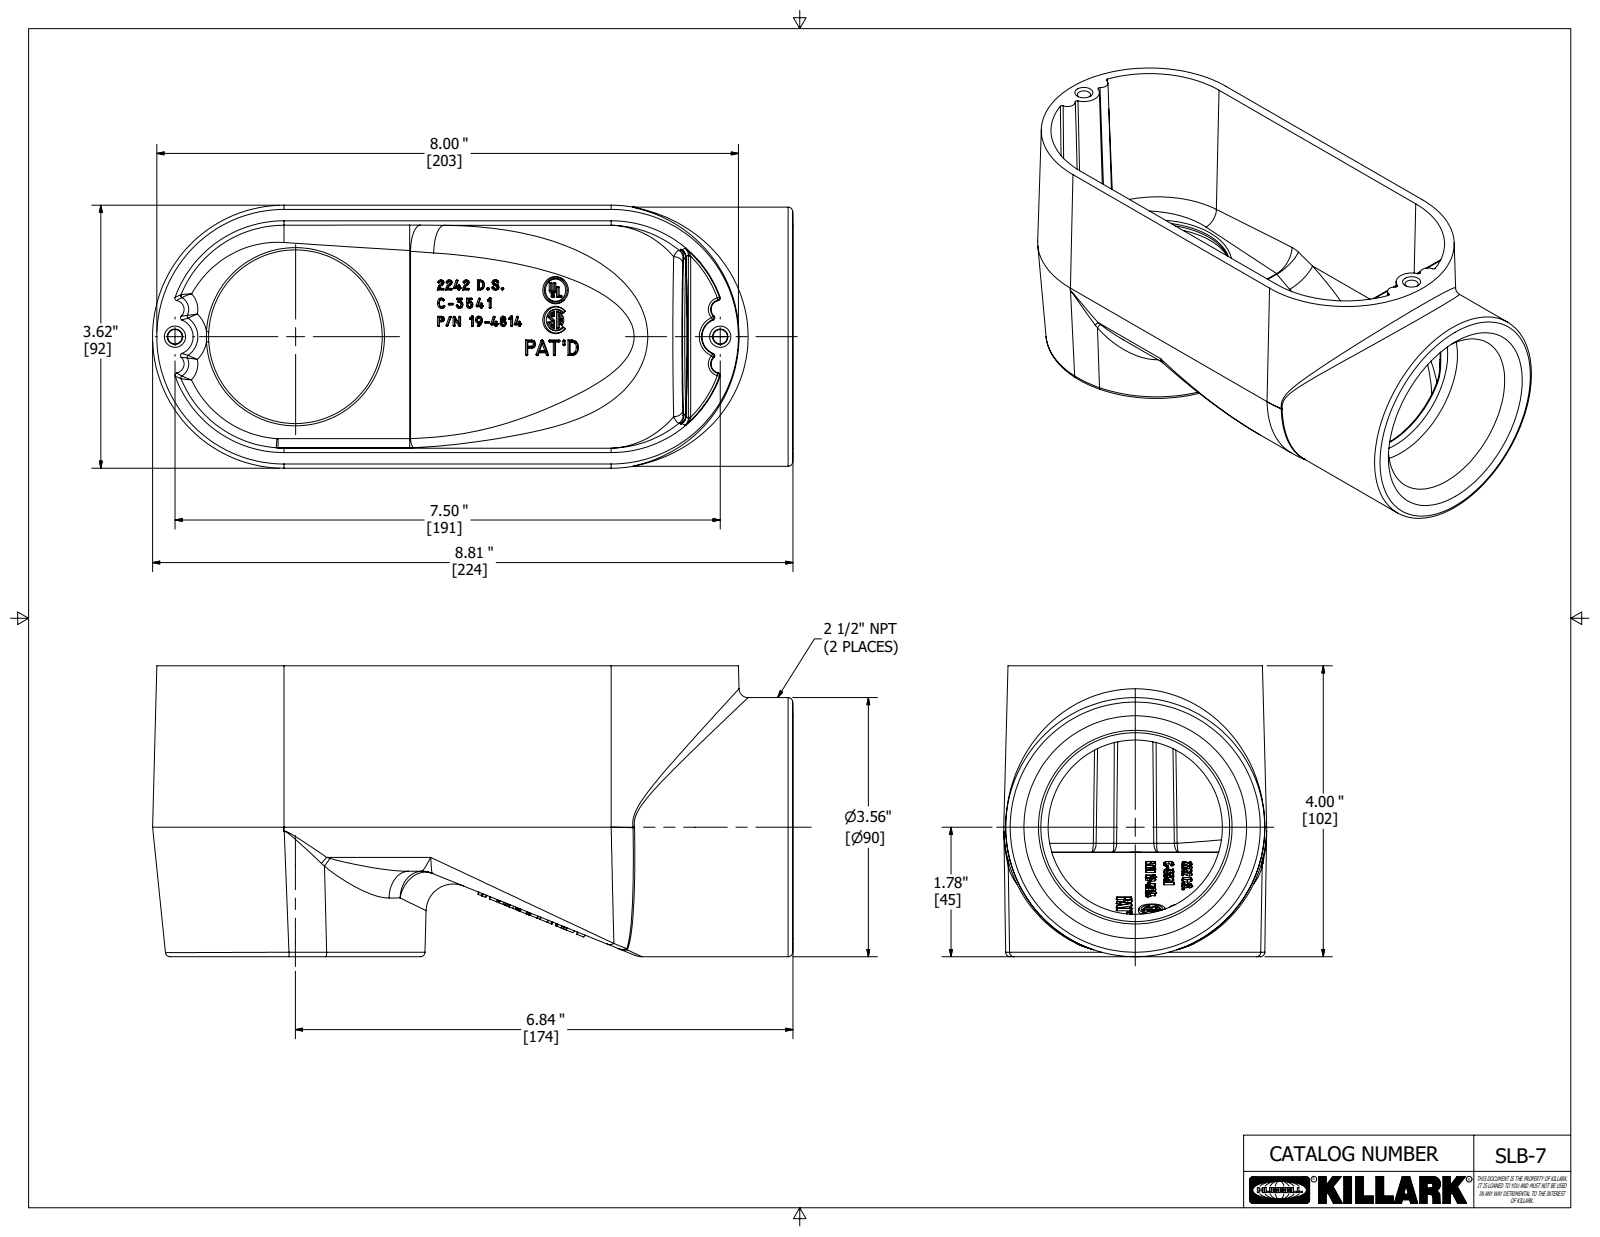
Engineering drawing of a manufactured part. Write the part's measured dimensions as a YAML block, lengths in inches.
part_name: "0194814 -2"
step_written_by: "Autodesk Inventor 2020 (AUTOMOTIVE_DESIGN)"
units: inches
bodies: {solids: 1, faces: 1087, planar: 384, cylindrical: 12, other: 691}
overall_size: [8.808, 4, 3.616]
volume: 27.84
surface_area: 194.1
round_holes:
  - {diameter: 2.396, count: 1}
round_bosses_or_shafts:
  - {diameter: 3.563, count: 1}
partial_cylinders:
  - {radius: 0.031, count: 2}
  - {radius: 0.25, count: 2}
  - {radius: 1.781, count: 2}
  - {radius: 0.004, count: 1}
  - {radius: 0.375, count: 1}
  - {radius: 1.533, count: 1}
face_to_face_distances: [3.344, 0.157, 2.563, 1.437, 4, 3.687, 2.25, 0.313, 0.031, 0.188]
